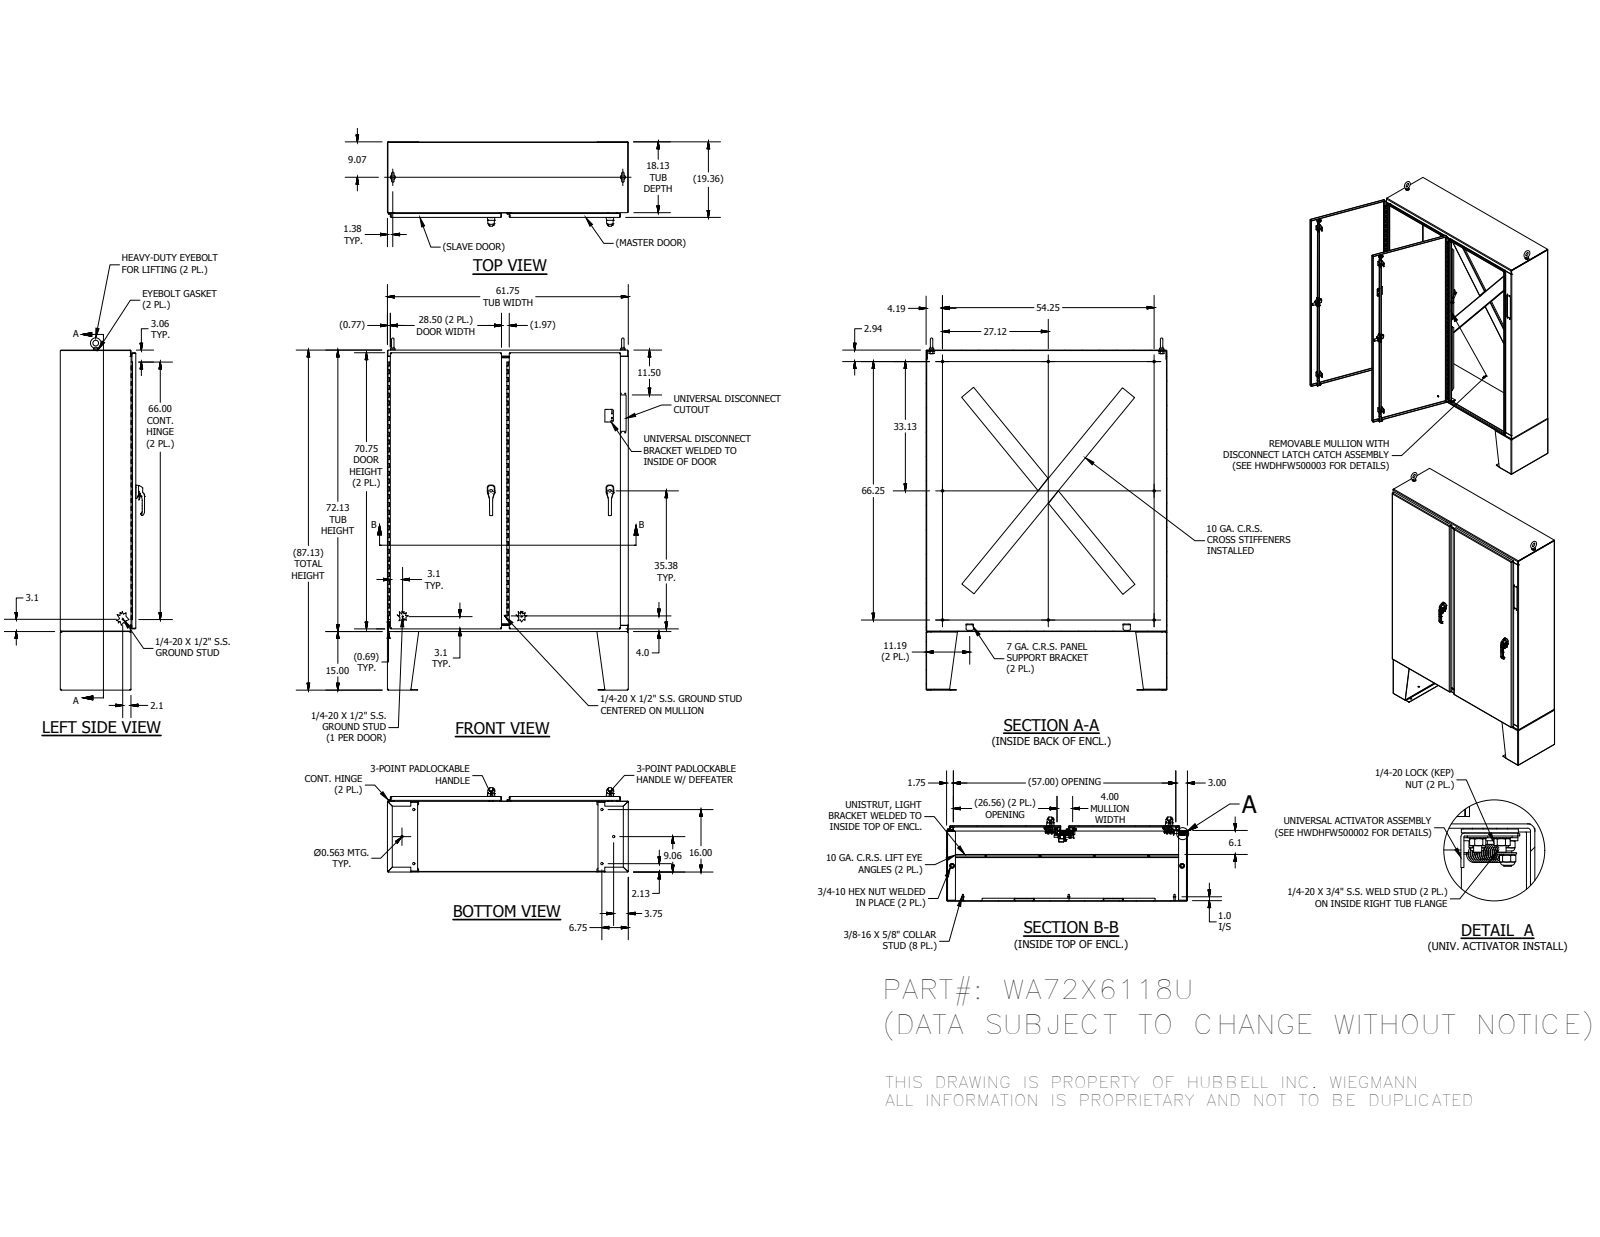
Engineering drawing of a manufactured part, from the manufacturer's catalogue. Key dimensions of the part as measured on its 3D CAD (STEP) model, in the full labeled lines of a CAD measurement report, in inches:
Part name (STEP PRODUCT): WA72X6118UBLR; WAX6118UTOP; WAX6118UBTM; HFW332010S (+8 more)
STEP written by: Autodesk Inventor 2016 (AUTOMOTIVE_DESIGN)
Units: inches
Bodies: 215 solids, 8901 faces (4144 planar, 2996 cylindrical, 1761 other)
Overall size (bounding box): 90.248 × 61.75 × 21.608
Volume: 2 381 in³ · Surface area: 36 970 in²
Round holes (diameter × count): ⌀0.25 ×18, ⌀0.375 ×18, ⌀0.563 ×18, ⌀0.19 ×8, ⌀0.2 ×8, ⌀0.203 ×8, ⌀0.276 ×8, ⌀0.289 ×8, ⌀0.313 ×8, ⌀0.335 ×8, ⌀0.38 ×8, ⌀0.201 ×7
Round bosses / shafts (diameter × count): ⌀0.25 ×24, ⌀0.33 ×18, ⌀0.625 ×13, ⌀0.337 ×12, ⌀0.375 ×11, ⌀0.563 ×9, ⌀1 ×8, ⌀0.438 ×8
Partial cylindrical surfaces — rounded edges, fillets, slot ends (radius × count): R0.02 ×339, R0.012 ×202, R0.02 ×192, R0.019 ×44, R0.094 ×41, R0.05 ×40, R0.125 ×37, R0.079 ×27
Main face-to-face distances: 0.134, 19.217, 19.083, 19.35, 0.134, 61.616, 71.991, 0.125, 61.482, 61.75
Hole centre spacings: 30.5, 0.03, 0.031, 1.102, 1.102, 2, 1.711, 30.513
